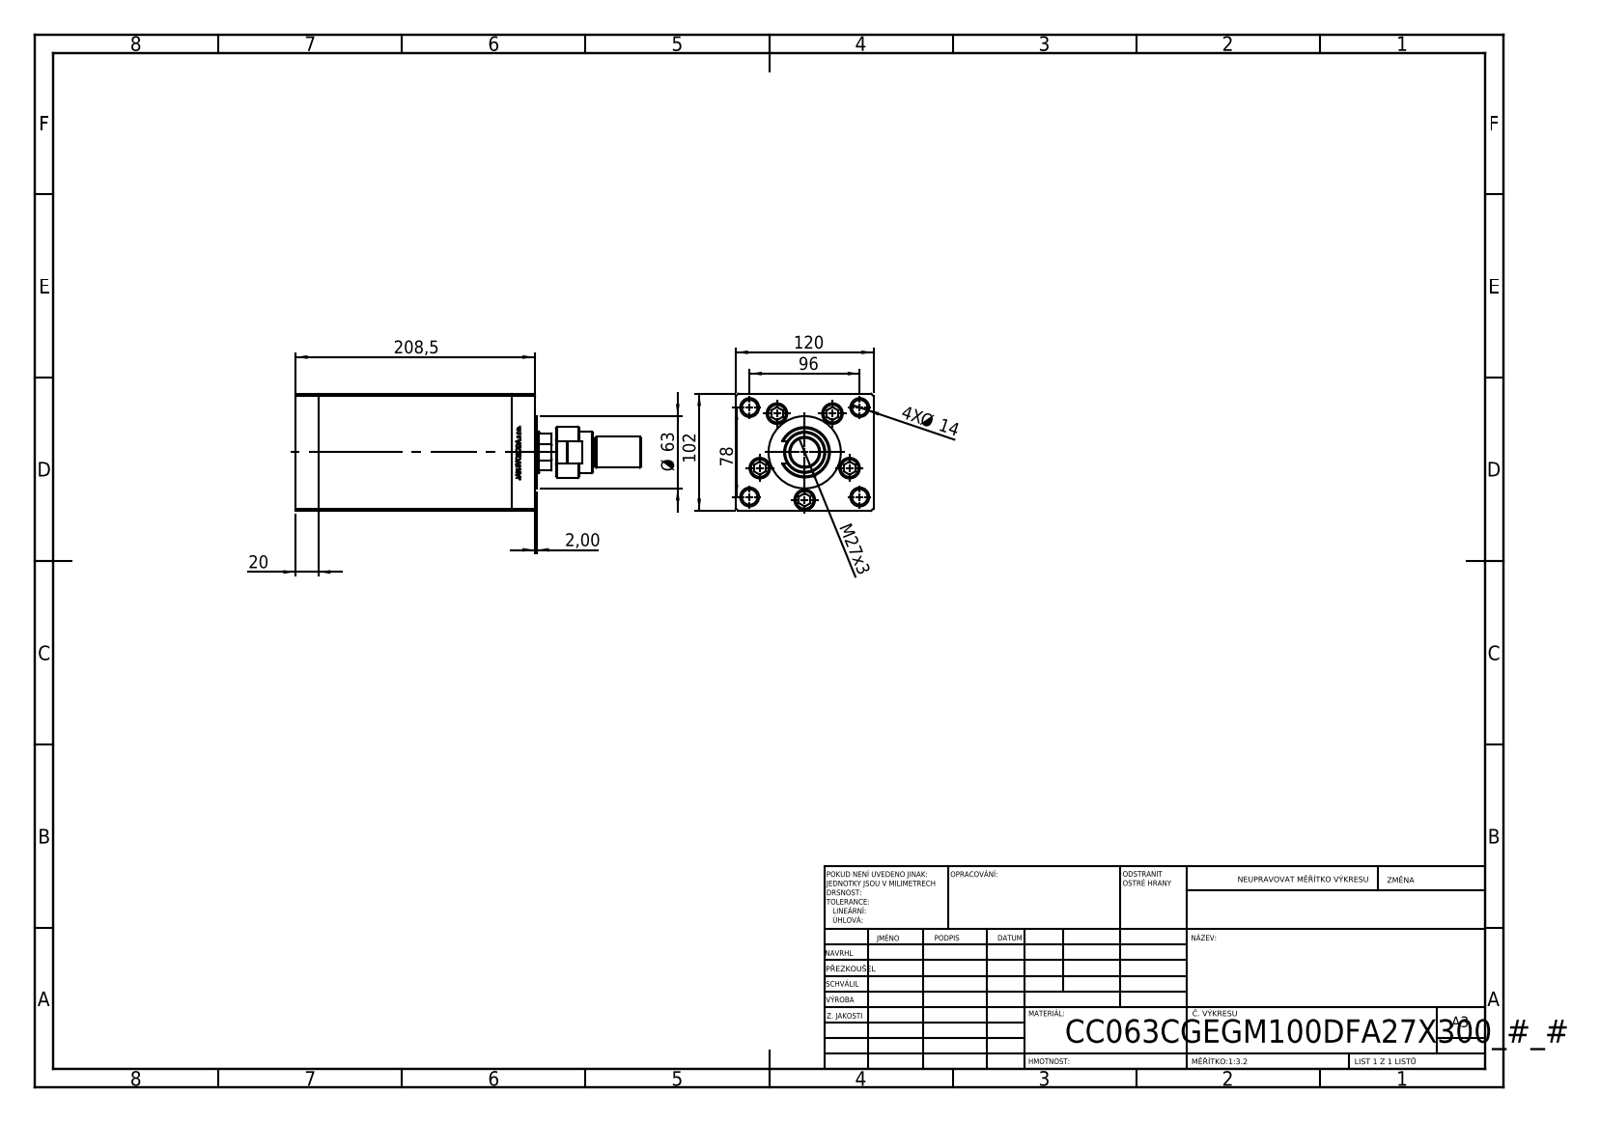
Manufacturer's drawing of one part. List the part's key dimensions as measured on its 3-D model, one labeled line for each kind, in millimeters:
Part name (STEP PRODUCT): V220C BACK_C; V220C_VC_C; V220C FRONT; V220C_C MIDDLE (+2 more)
STEP written by: SolidWorks 2019 (CONFIG_CONTROL_DESIGN)
Units: millimetres
Bodies: 14 solids, 1198 faces (554 planar, 170 cylindrical, 474 other)
Overall size (bounding box): 301.3 × 120 × 102
Volume: 2 191 000 mm³ · Surface area: 310 768 mm²
Round holes (diameter × count): ⌀13.5 ×9, ⌀18 ×5, ⌀12 ×4, ⌀16.5 ×4, ⌀17 ×1, ⌀25.5 ×1
Round bosses / shafts (diameter × count): ⌀8 ×5, ⌀17 ×4, ⌀63 ×1, ⌀44 ×1, ⌀36 ×1, ⌀27 ×1, ⌀25 ×1
Partial cylindrical surfaces — rounded edges, fillets, slot ends (radius × count): R0.93 ×2, R9.5 ×1, R15 ×1, R17.5 ×1
Main face-to-face distances: 120, 102, 20, 168.5, 188.5, 34.25, 208.5, 174.25, 154.25, 14.25
Hole centre spacings: 41.5, 61.85, 24.39, 26.69, 47.92, 48.07, 49.84, 53.57
